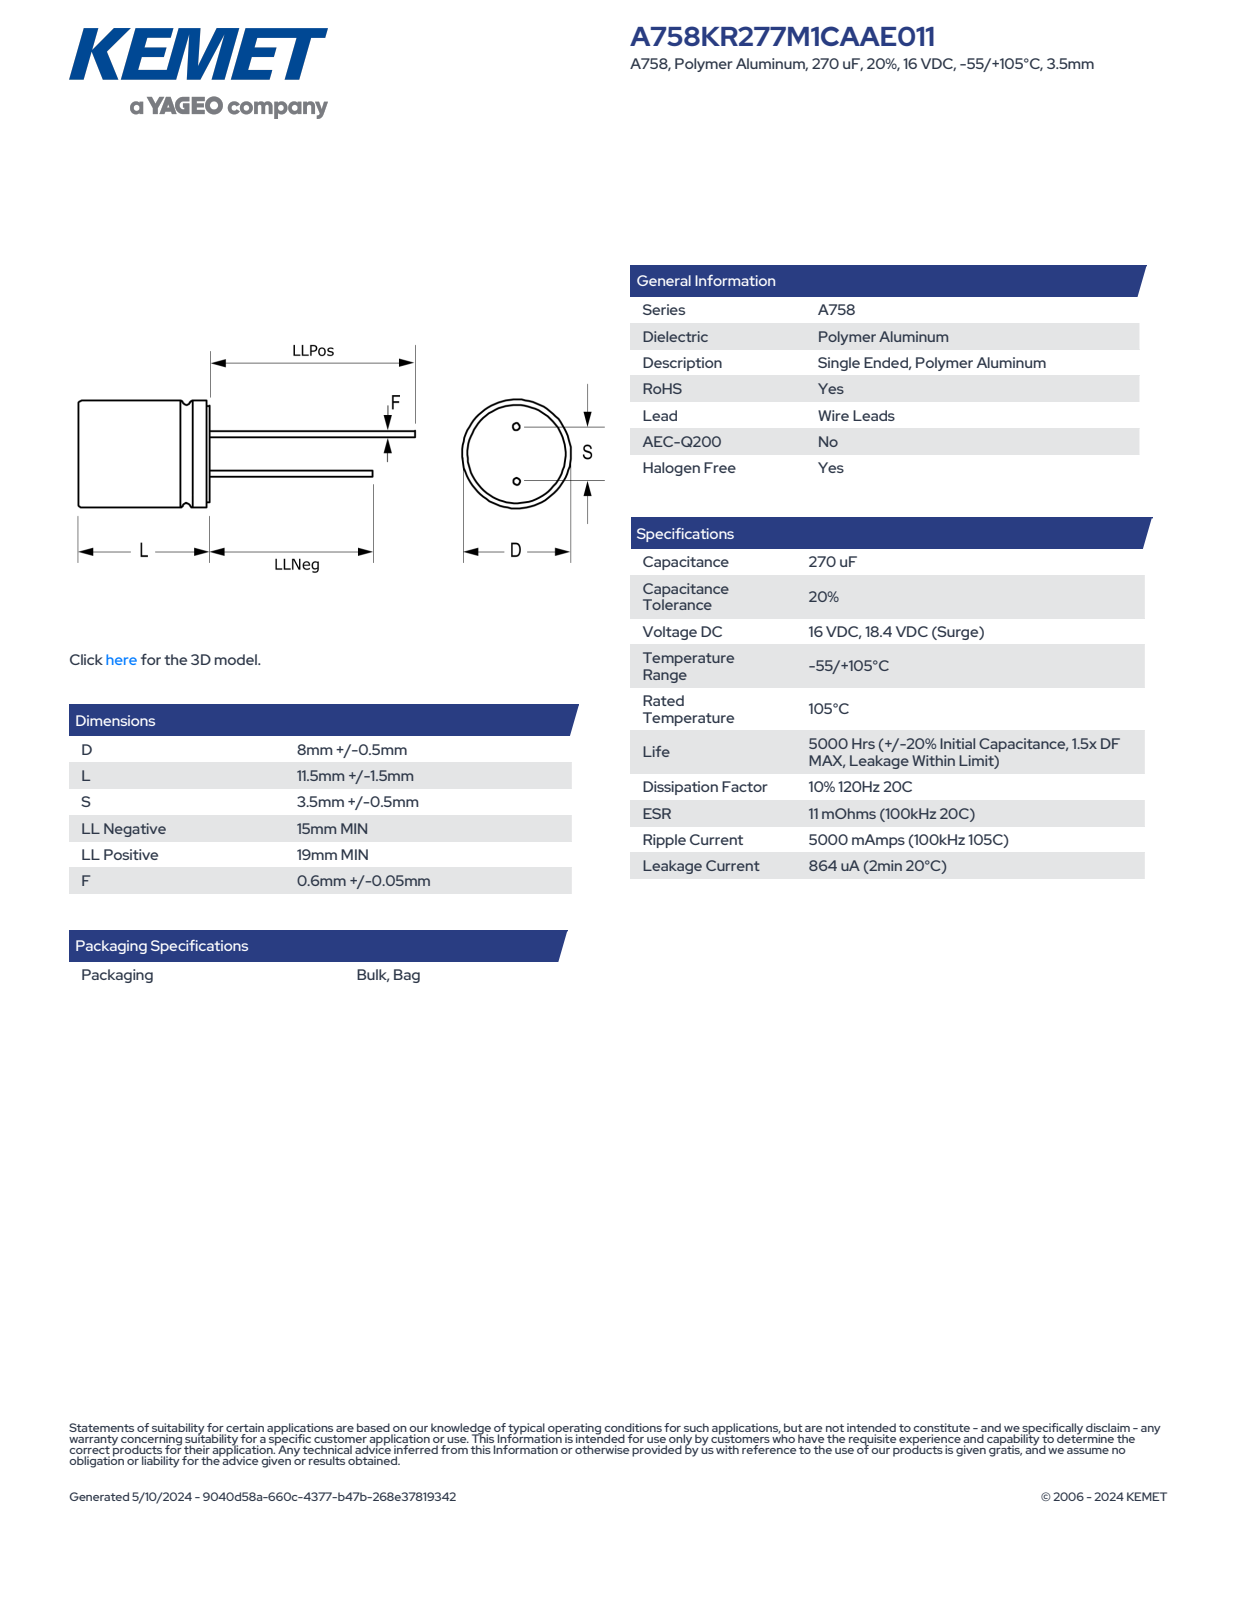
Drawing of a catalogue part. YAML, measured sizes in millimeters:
part_name: "CAR_KP_8X11.5_D8.5L13S3.5F0.65"
step_written_by: "SolidWorks 2014 (AUTOMOTIVE_DESIGN)"
units: millimeters
bodies: {solids: 4, faces: 75, planar: 61, cylindrical: 8, other: 6}
overall_size: [32.01, 8.5, 8.5]
volume: 742
surface_area: 543
round_bosses_or_shafts:
  - {diameter: 0.65, count: 2}
  - {diameter: 8.5, count: 1}
face_to_face_distances: [13, 13.01, 28.01, 32.01, 28, 32, 15, 19, 4, 0.93]
